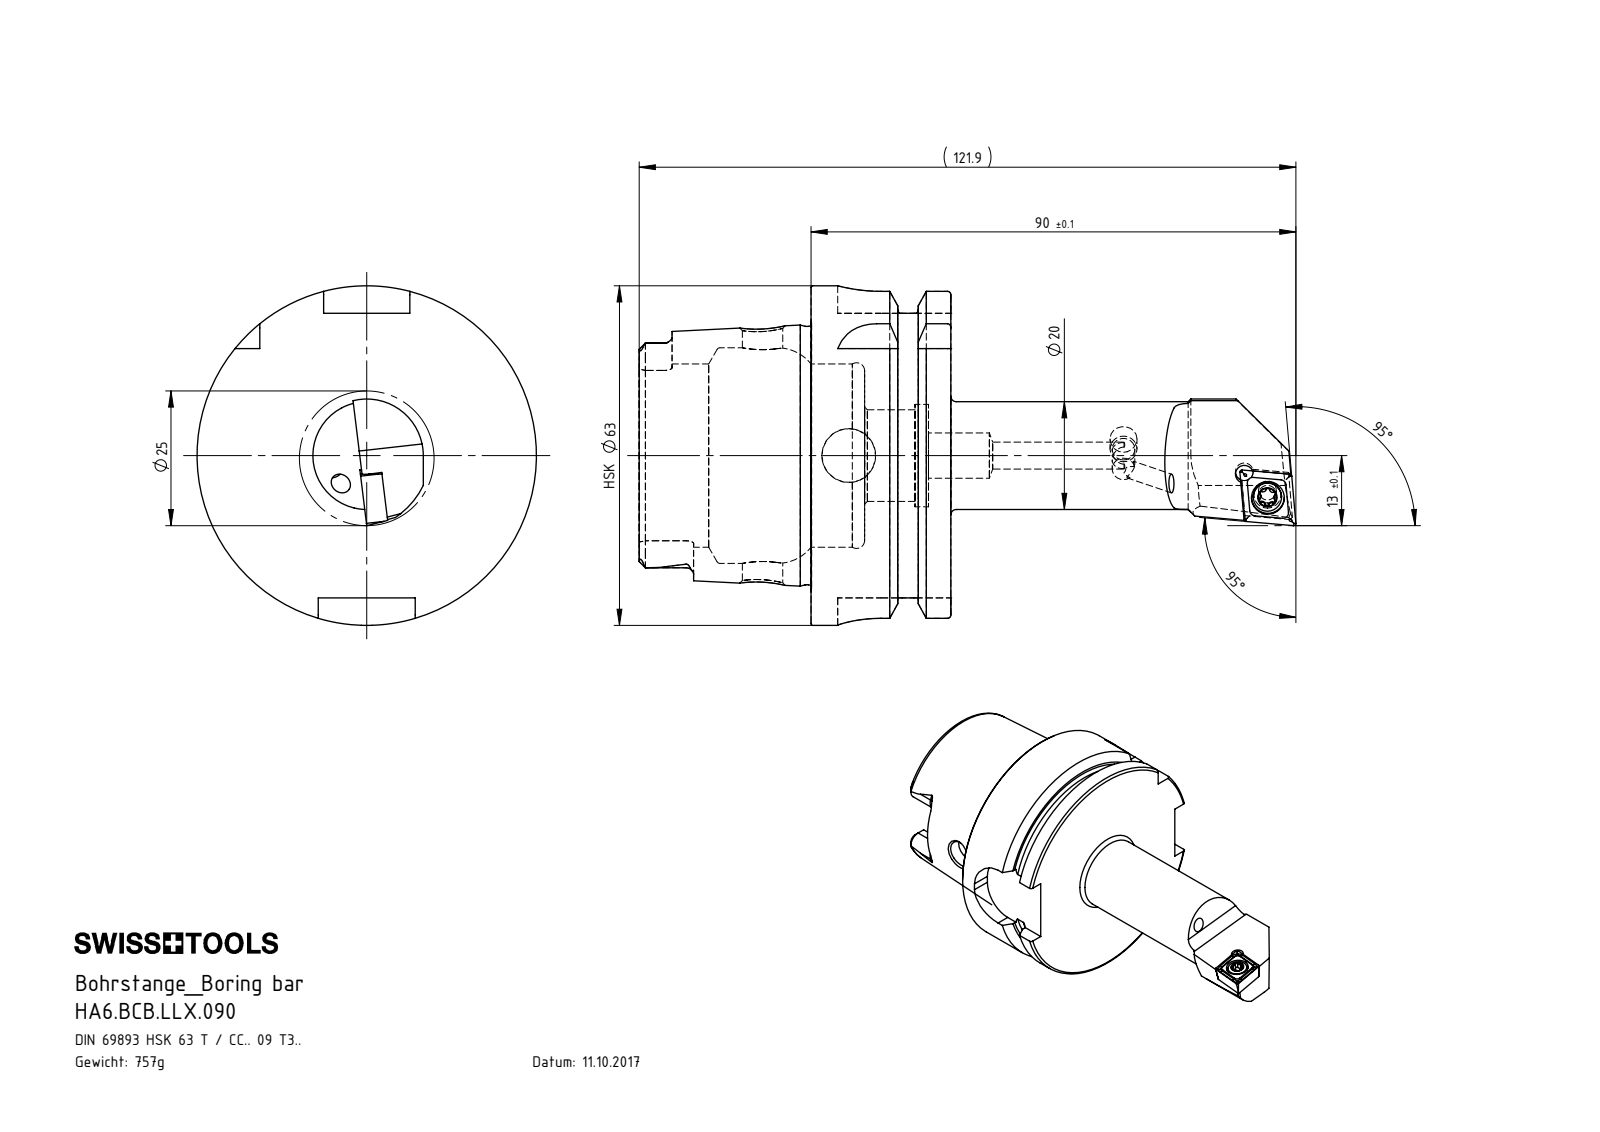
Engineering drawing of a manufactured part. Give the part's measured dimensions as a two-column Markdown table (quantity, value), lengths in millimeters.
| quantity | value |
| --- | --- |
| part name | HA6.BCB.LLX.090; CCMT09T304; WCB-ER2.001.009_A; KVT_MB_600_050 (+1 more) |
| STEP written by | SolidWorks 2017 (AUTOMOTIVE_DESIGN) |
| units | millimeters |
| bodies | 5 solids, 313 faces (78 planar, 91 cylindrical, 144 other) |
| overall size | 121.9 × 63 × 63 |
| volume | 96 393 mm³ |
| surface area | 27 830 mm² |
| round holes (diameter × count) | 3.3 × 3, 4 × 1, 4.2 × 1, 4.4 × 1, 5 × 1, 6.1 × 1, 7.5 × 1, 8.4 × 1, 10 × 1, 17 × 1, 19 × 1, 34 × 1 |
| round bosses / shafts (diameter × count) | 63 × 1, 54.95 × 1, 47.94 × 1, 20 × 1, 5.25 × 1, 5 × 1, 4 × 1 |
| partial cylindrical surfaces (radius × count) | 0.34 × 6, 0.59 × 6, 1.4 × 6, 8 × 4, 2.82 × 2, 2.88 × 2, 3 × 1, 10.5 × 1 |
| main face-to-face distances | 25.95, 16, 9.95, 31.9, 41.85, 57.85, 52.8, 21.8, 11.85, 53.7 |
| hole center spacings | 6.06, 6.19 |
